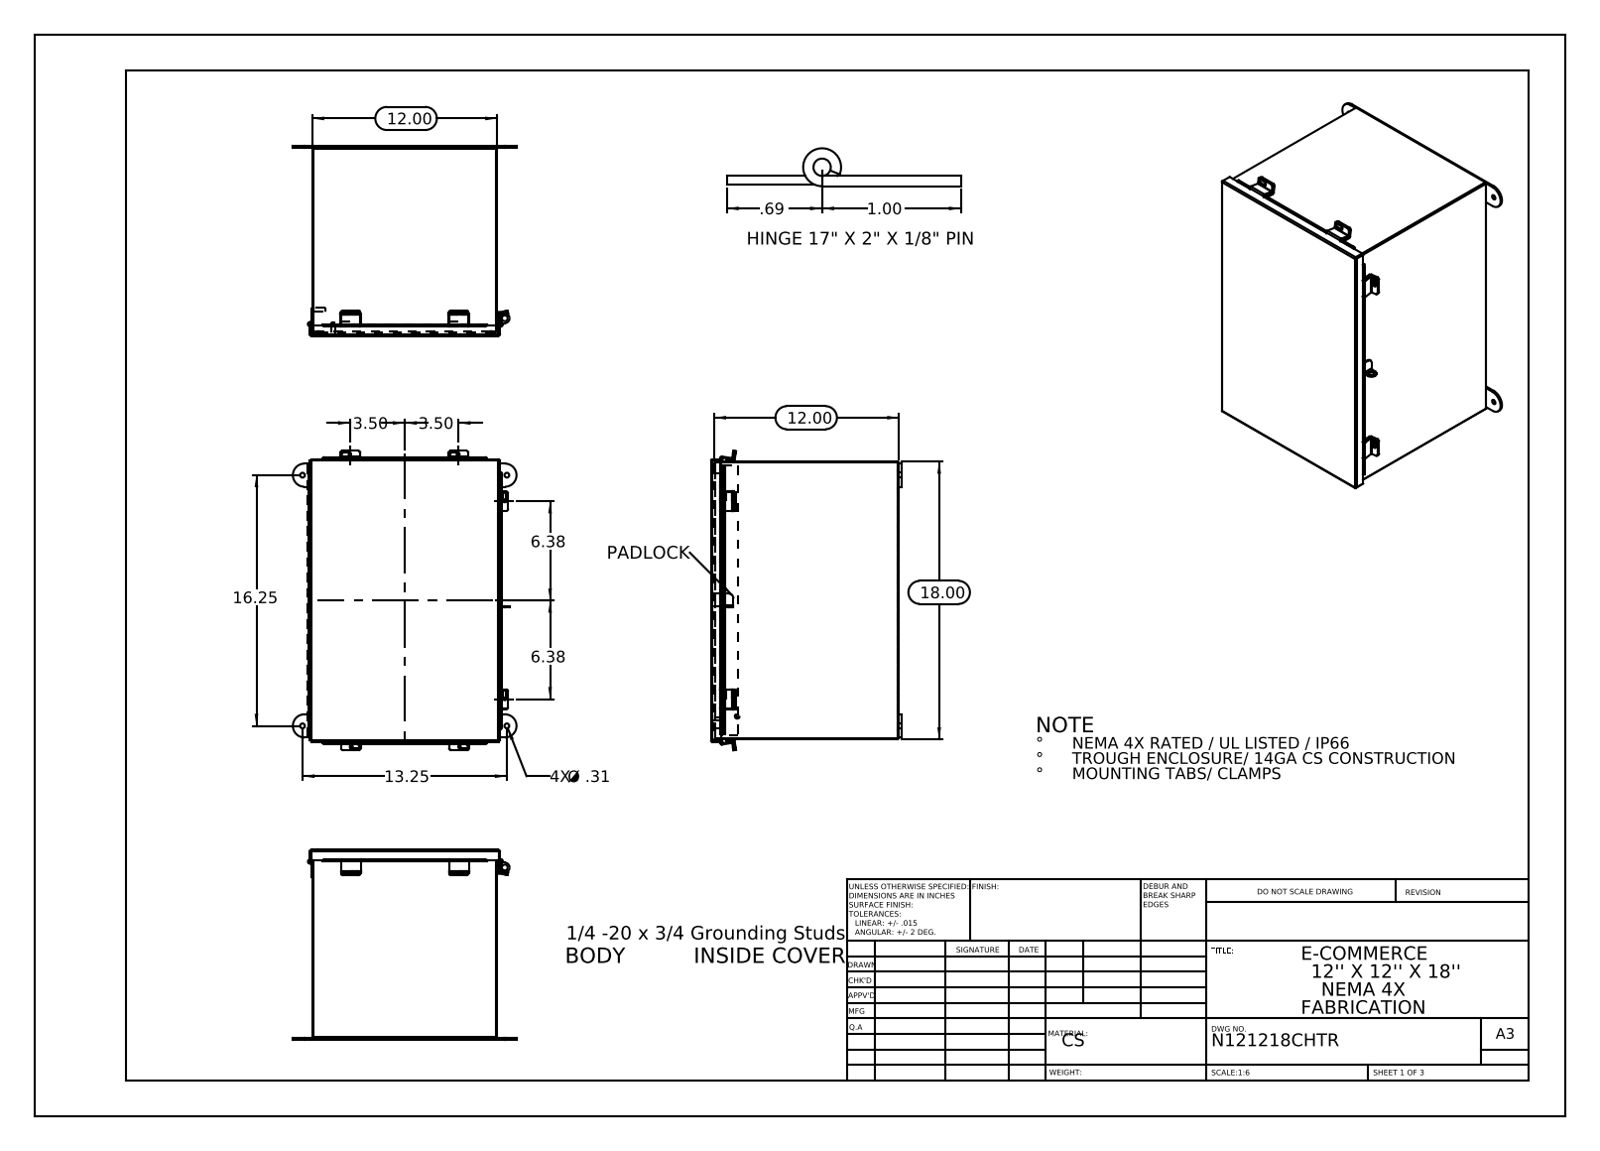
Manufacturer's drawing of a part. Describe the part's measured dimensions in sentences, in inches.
The part is named "N121218SSCHTR JIC Bottom; N121218SSCHTR JIC_Cover_Template; N121218SSCHTR JIC Cover Clamp; N121218SSCHTR JIC Enclosure Template (+8 more)". Its 3-D file was written by "SolidWorks 2013 (CONFIG_CONTROL_DESIGN)". It is 23 solids with 836 faces: 525 planar, 291 cylindrical and 20 other. Overall it measures 19.407 by 14.5 by 12.337 inches. Its volume is 99.89 cubic inches and its surface area 2 650 square inches. Round holes: 6 of diameter 0.25, 4 of diameter 0.313, 1 of diameter 0.125, 1 of diameter 0.125, 1 of diameter 0.375. Round bosses or shafts: 2 of diameter 0.315, 2 of diameter 0.236, 1 of diameter 0.273, 1 of diameter 0.25. Partial cylindrical surfaces (rounded edges, fillets, slot ends): 21 of radius 0.125, 12 of radius 0.009, 12 of radius 0.133, 10 of radius 0.013, 10 of radius 0.088, 6 of radius 0.083, 6 of radius 0.1, 4 of radius 0.75. The main face-to-face distances are 0.075, 11.925, 12.128, 17.925, 11.85, 12, 12.203, 12.053, 17.85, 18. The hole center spacings are 7, 13.25, 16.25, 20.968, 12.632, 12.85.
